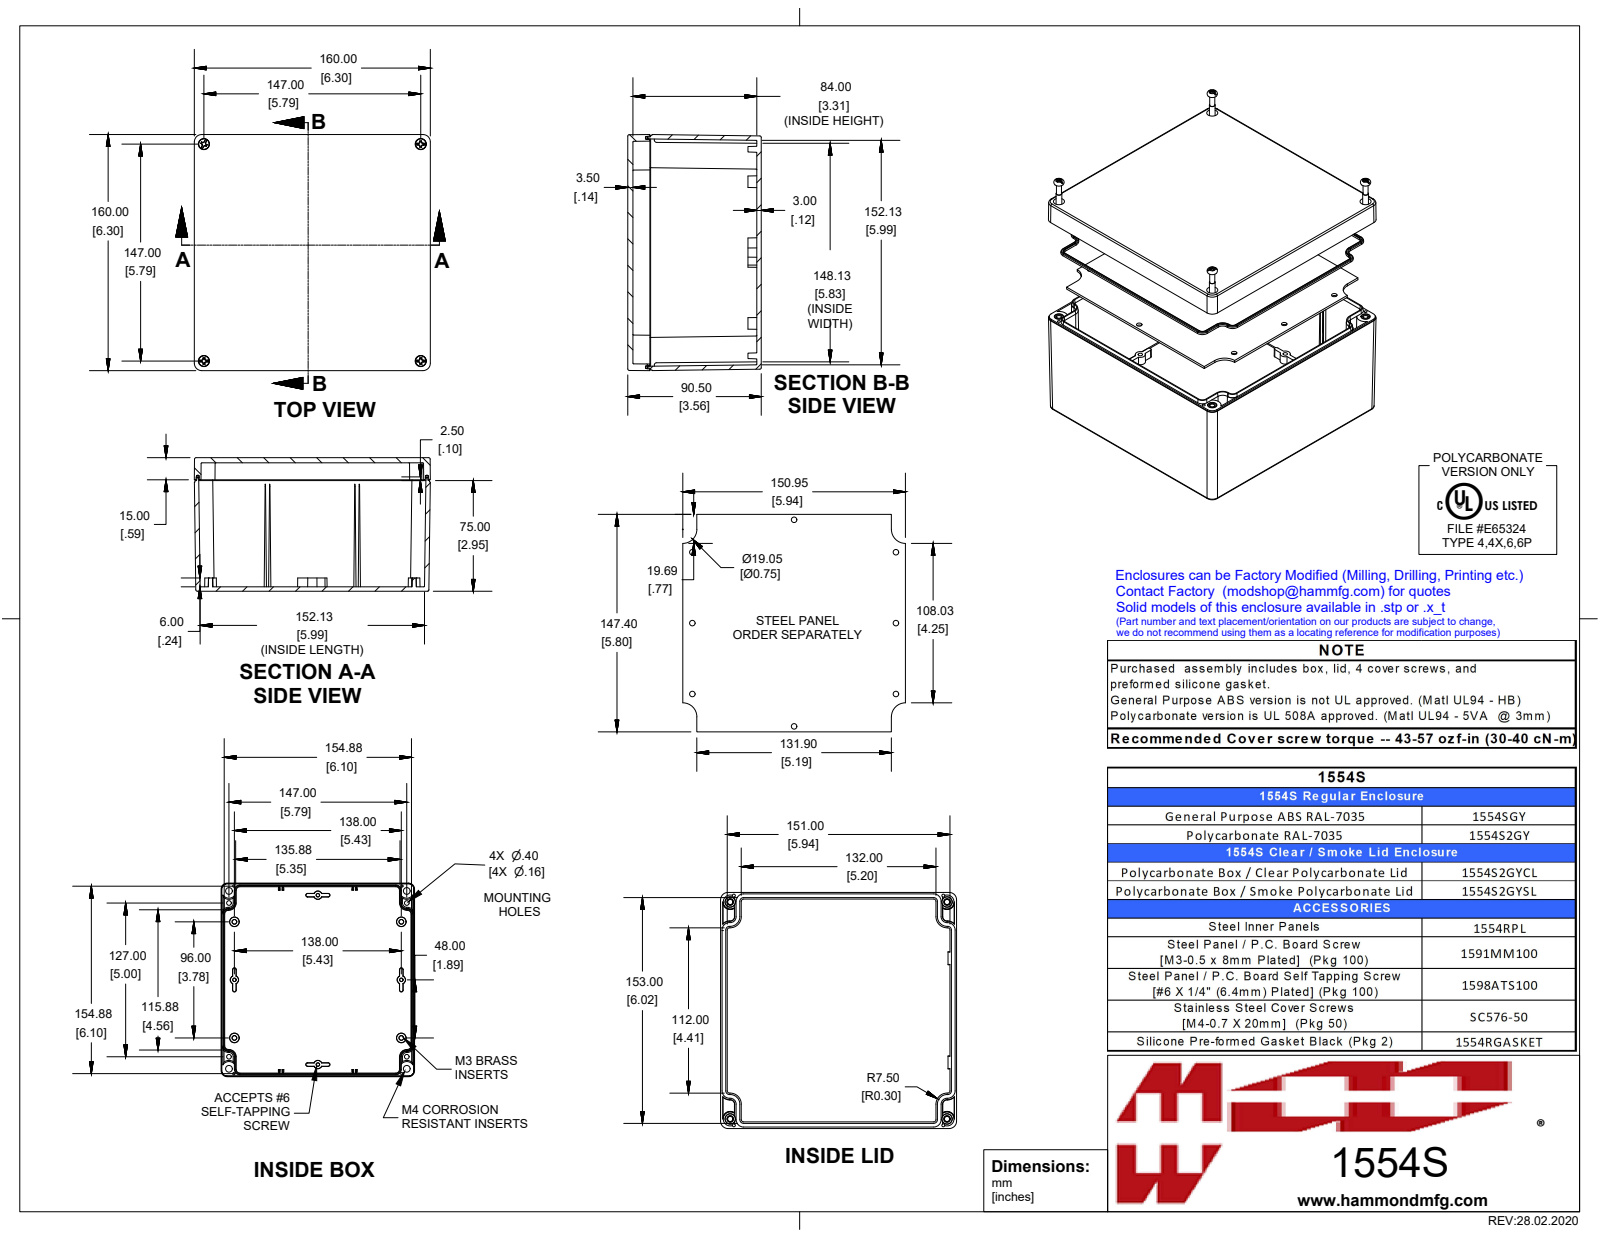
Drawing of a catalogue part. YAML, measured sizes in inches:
part_name: "1554SGY"
step_written_by: "SolidWorks 2019 (AUTOMOTIVE_DESIGN)"
units: inches
bodies: {solids: 16, faces: 1384, planar: 392, cylindrical: 352, other: 640}
overall_size: [6.299, 6.299, 3.563]
volume: 23.92
surface_area: 446
round_holes:
  - {diameter: 0.079, count: 8}
  - {diameter: 0.097, count: 4}
  - {diameter: 0.11, count: 4}
  - {diameter: 0.128, count: 4}
  - {diameter: 0.138, count: 4}
  - {diameter: 0.147, count: 4}
  - {diameter: 0.276, count: 4}
round_bosses_or_shafts:
  - {diameter: 0.25, count: 4}
  - {diameter: 0.218, count: 4}
  - {diameter: 0.21, count: 4}
  - {diameter: 0.19, count: 4}
  - {diameter: 0.154, count: 4}
  - {diameter: 0.153, count: 4}
  - {diameter: 0.15, count: 4}
  - {diameter: 0.135, count: 4}
partial_cylinders:
  - {radius: 0.02, count: 44}
  - {radius: 0.039, count: 8}
  - {radius: 0.197, count: 8}
  - {radius: 0.187, count: 4}
  - {radius: 0.375, count: 4}
  - {radius: 0.059, count: 2}
face_to_face_distances: [0.118, 3.563, 0.138, 0.354, 3.209, 3.425, 3.307, 0.236, 3.445, 3.071]
hole_center_spacings: [5.433, 2.851, 5.635, 5.699, 0.197, 1.019, 1.019, 1.176]
